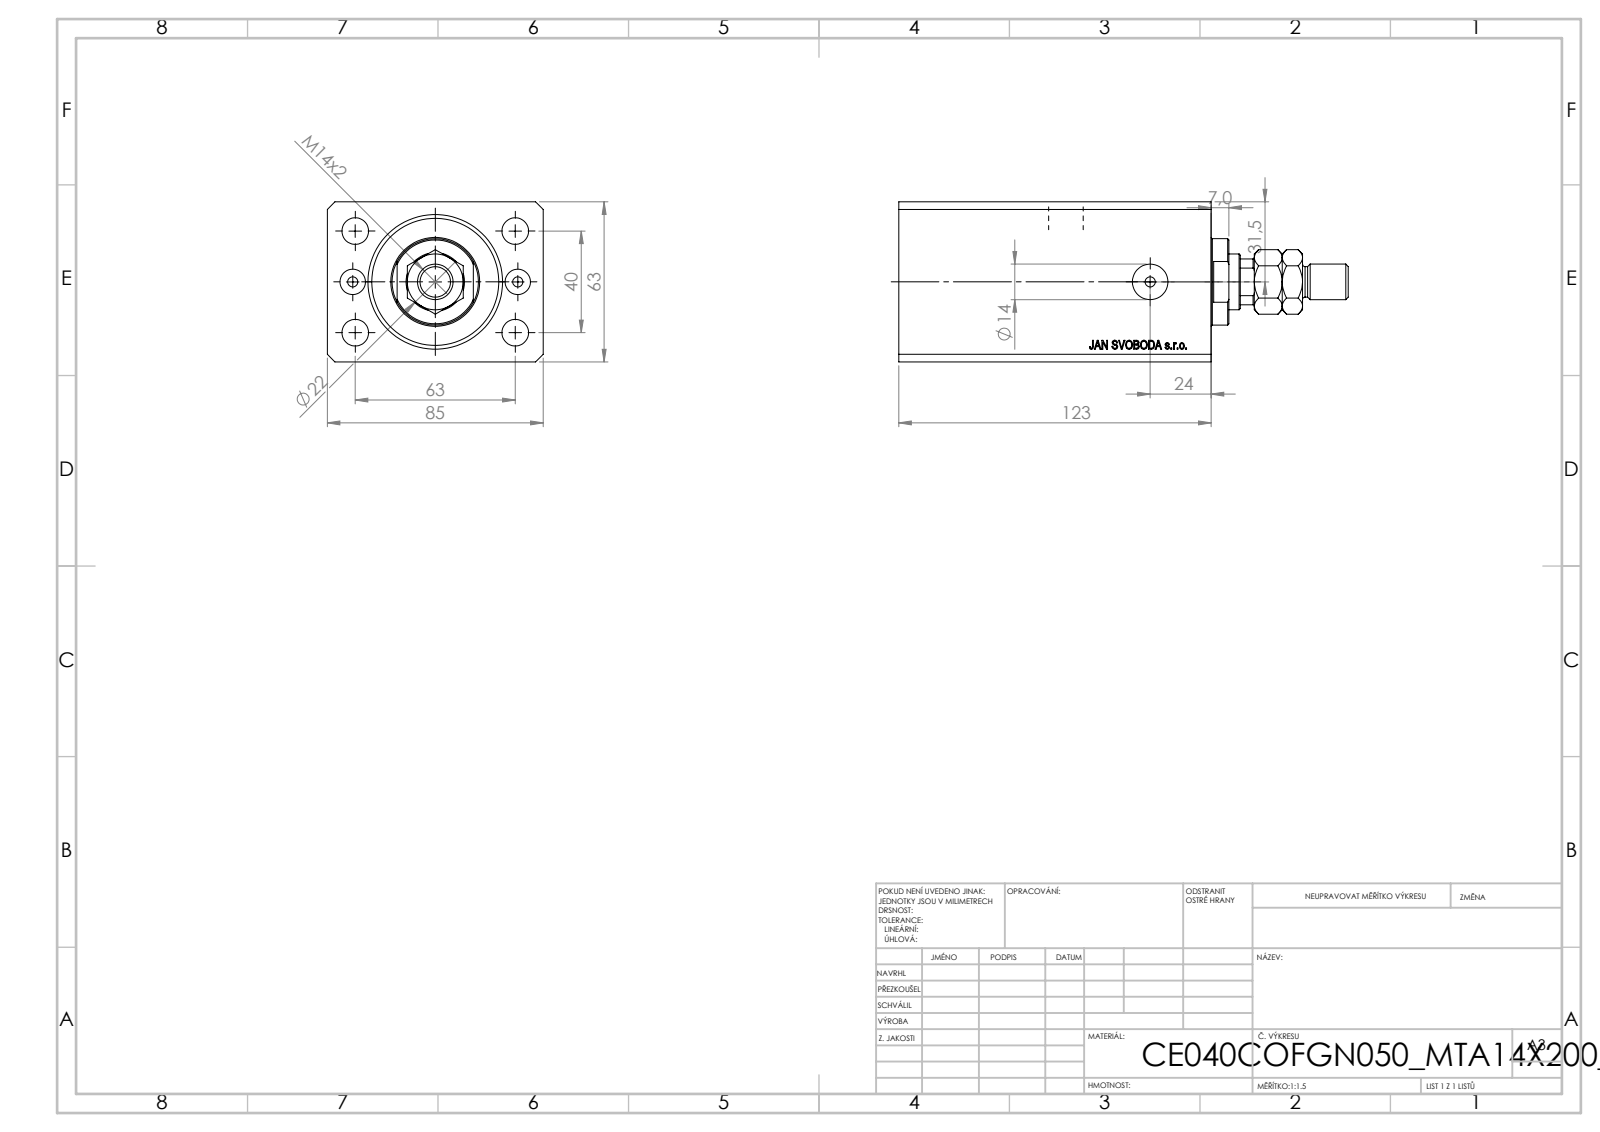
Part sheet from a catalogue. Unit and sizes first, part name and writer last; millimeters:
Units: millimetres
Overall size (bounding box): 177 × 85 × 63
Round holes (diameter × count): ⌀4 ×4, ⌀10.5 ×4, ⌀10 ×2, ⌀14 ×2, ⌀12.5 ×1, ⌀22 ×1, ⌀40 ×1, ⌀53 ×1
Round bosses / shafts (diameter × count): ⌀34 ×1, ⌀14 ×1, ⌀12 ×1
Partial cylindrical surfaces — rounded edges, fillets, slot ends (radius × count): R10.5 ×1
Main face-to-face distances: 63, 85, 123, 17, 106, 11.4, 94.6, 111.6, 100.4, 50
Hole centre spacings: 20.02, 37.31, 67.05, 32.5, 40, 63, 74.63, 65
Volume: 584 018 mm³ · Surface area: 105 166 mm²
Bodies: 4 solids, 913 faces (443 planar, 48 cylindrical, 422 other)
Part name (STEP PRODUCT): V250CE_C_VCP; V250CE_VC_C; MTA; V250CE_C_Body
STEP written by: SolidWorks 2019 (CONFIG_CONTROL_DESIGN)
